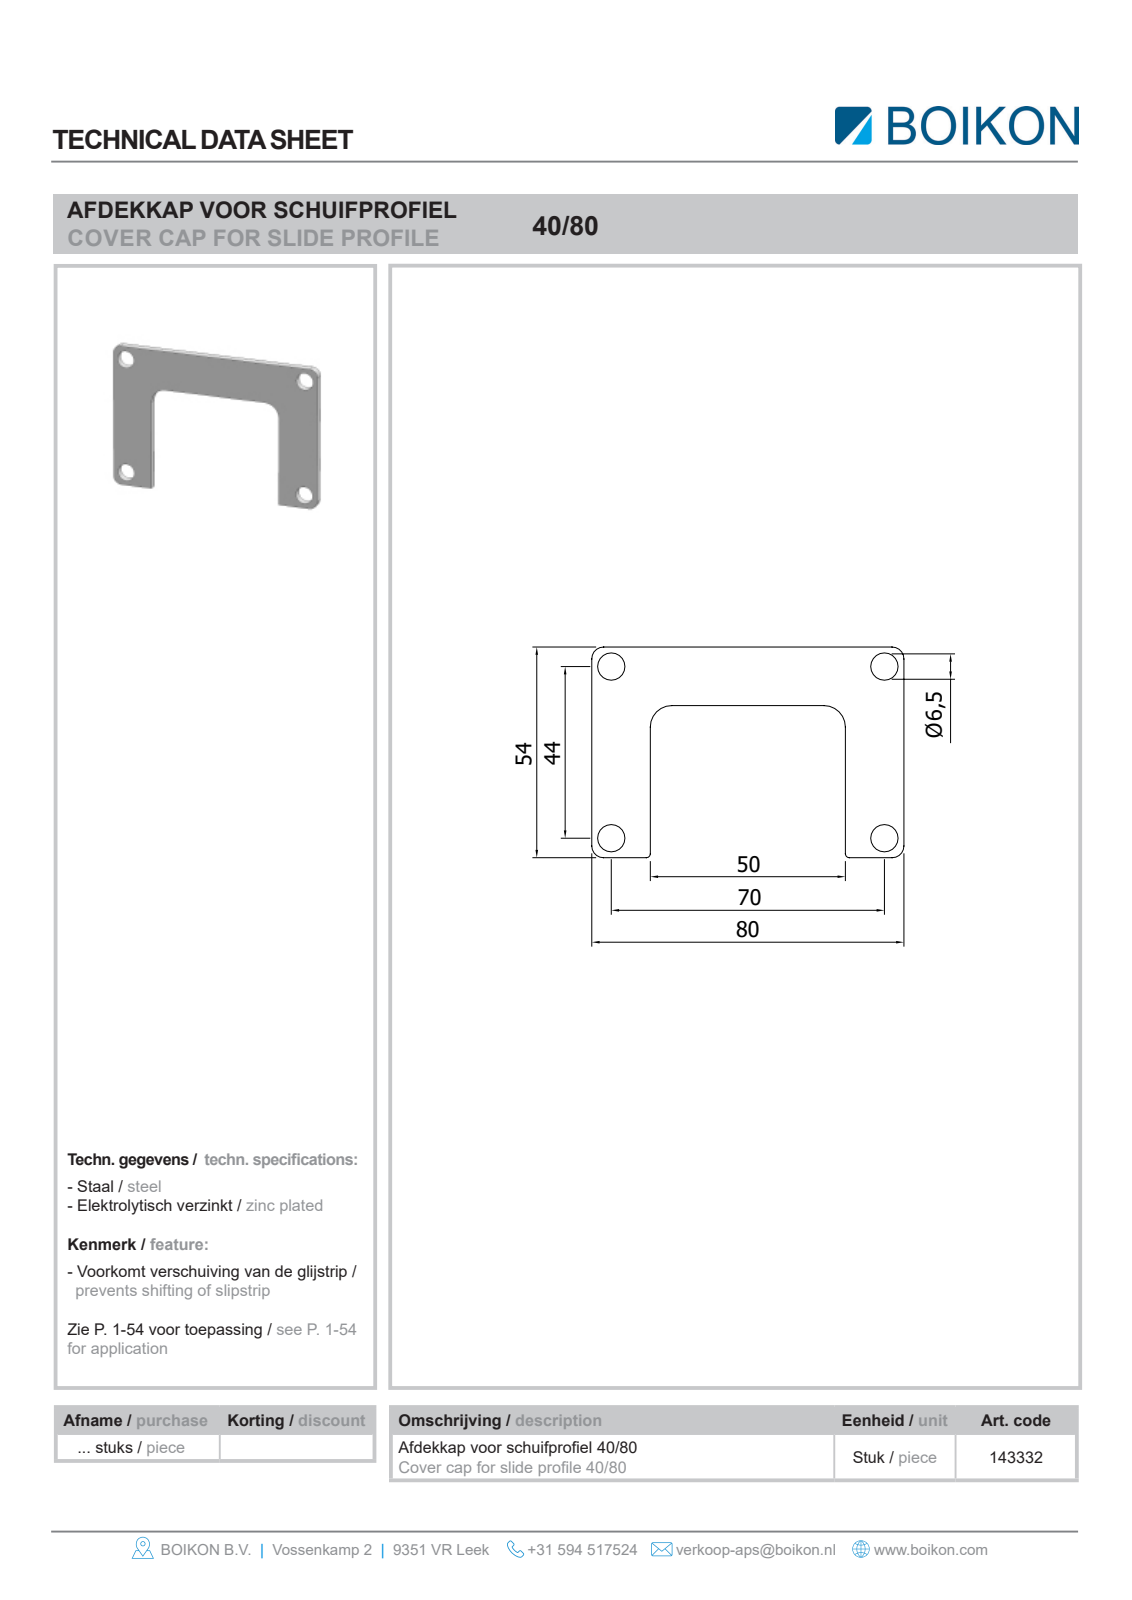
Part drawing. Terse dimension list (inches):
name: Root; 143332Afdekkap voor schuifprofiel 40-80BOIKON0; 120030Laagbolkopschroef M6 x 16Pan head bolts0
written by: HiCAD 2013 1802.4 Build 509 (AUTOMOTIVE_DESIGN)
unit: in
bodies: 5 solids, 76 faces (50 planar, 18 cylindrical, 8 other)
size: 3.169 × 2.146 × 0.76
volume: 0.524 in³; area: 11.91 in²
holes: 4× ⌀0.256
bosses: 4× ⌀0.236, 3× ⌀0.188, 1× ⌀0.188
rounds: 4× R0.118, 2× R0.217
face distances: 0.118, 0.591, 2.559, 3.15, 1.969, 1.535, 2.126, 0.512, 0.63, 0.157
hole spacings: 1.732, 2.756, 3.255
